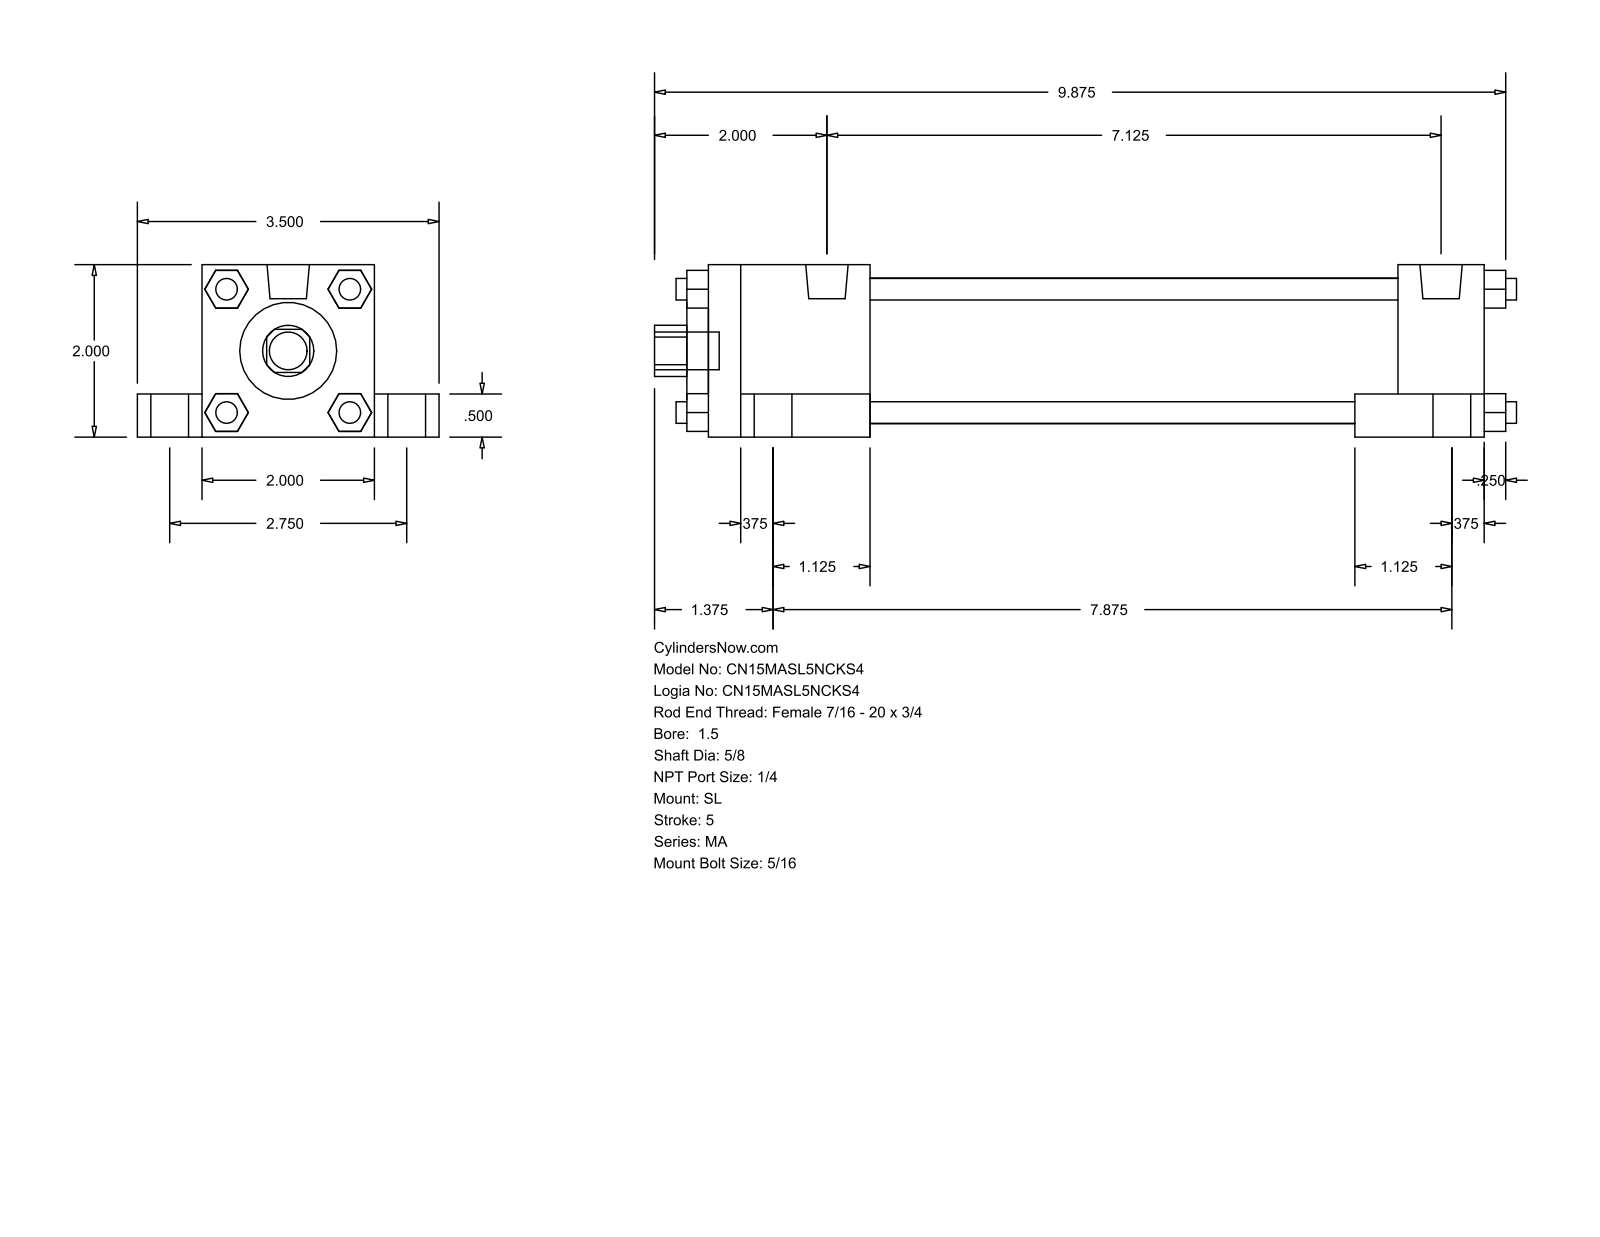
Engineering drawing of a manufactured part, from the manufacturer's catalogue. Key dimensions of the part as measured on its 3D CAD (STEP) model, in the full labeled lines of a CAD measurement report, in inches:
Part name (STEP PRODUCT): MA_SL__0150_0.625
STEP written by: GSSL Pune (CONFIG_CONTROL_DESIGN)
Units: inches
Bodies: 0 solids, 148 faces (112 planar, 36 cylindrical, 0 other)
Overall size (bounding box): 10 × 3.5 × 2
Round holes (diameter × count): ⌀0.625 ×1, ⌀1.125 ×1, ⌀1.69 ×1
Round bosses / shafts (diameter × count): ⌀0.437 ×5, ⌀0.687 ×4, ⌀0.313 ×4, ⌀0.25 ×4, ⌀0.492 ×2
Partial cylindrical surfaces — rounded edges, fillets, slot ends (radius × count): R0.297 ×1
Main face-to-face distances: 2, 0.75, 1.5, 0.5, 2.75, 9, 6.125, 0.25, 0.375, 1
